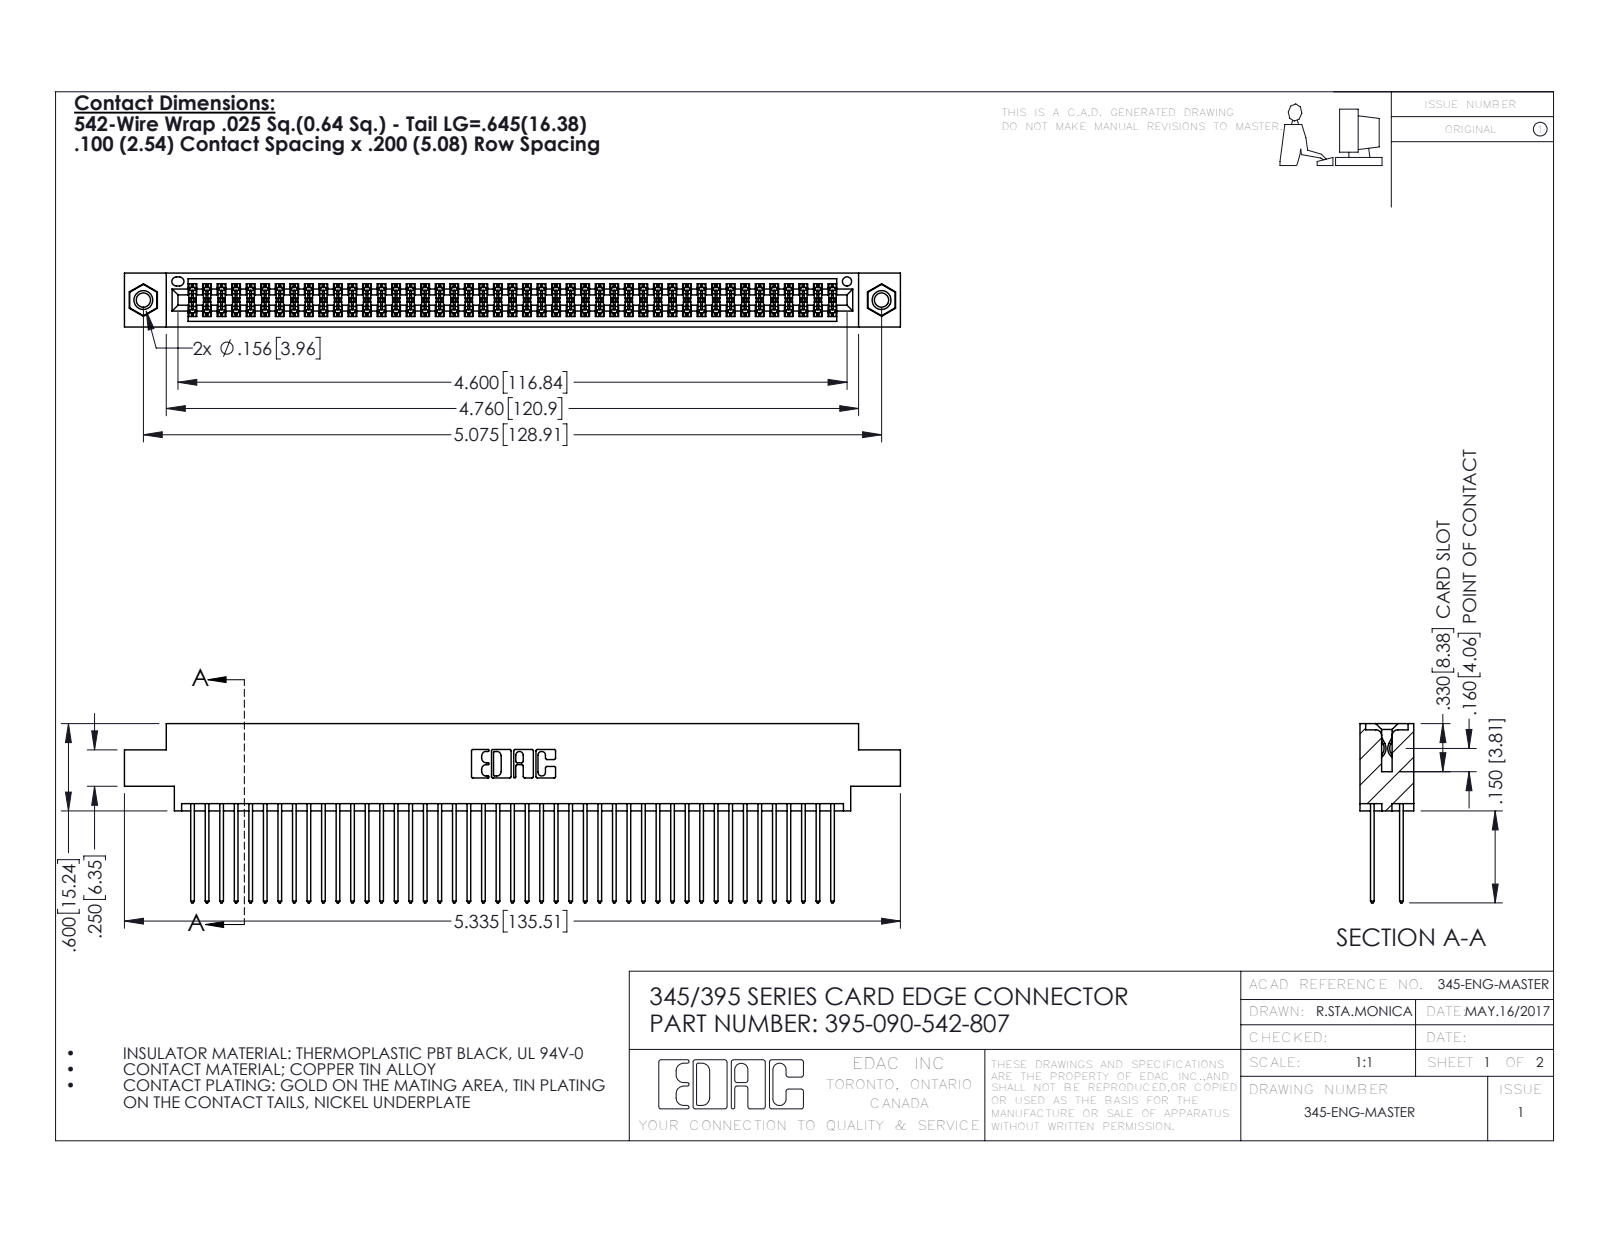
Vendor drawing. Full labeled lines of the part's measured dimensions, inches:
Part name (STEP PRODUCT): 345-250-001_345-250-005-103; 395-090-542-807; 345 Part_0.170 Offset - 0.156 Dia-TI; 345-292-001_345-293-142
STEP written by: SolidWorks 2016 (CONFIG_CONTROL_DESIGN)
Units: inches
Bodies: 93 solids, 4690 faces (3086 planar, 1588 cylindrical, 16 other)
Overall size (bounding box): 5.335 × 1.232 × 0.37
Volume: 0.823 in³ · Surface area: 34.29 in²
Round holes (diameter × count): ⌀0.098 ×2, ⌀0.125 ×2, ⌀0.156 ×2, ⌀0.064 ×1
Round bosses / shafts (diameter × count): ⌀0.155 ×2
Partial cylindrical surfaces — rounded edges, fillets, slot ends (radius × count): R0.006 ×135, R0.01 ×90, R0.01 ×22, R0.007 ×6, R0.031 ×6, R0.026 ×3, R0.014 ×2, R0.019 ×2
Main face-to-face distances: 0.072, 0.298, 0.2, 0.098, 0.272, 0.025, 0.37, 0.225, 0.175, 0.149
Hole centre spacings: 0.27, 4.839, 5.075
